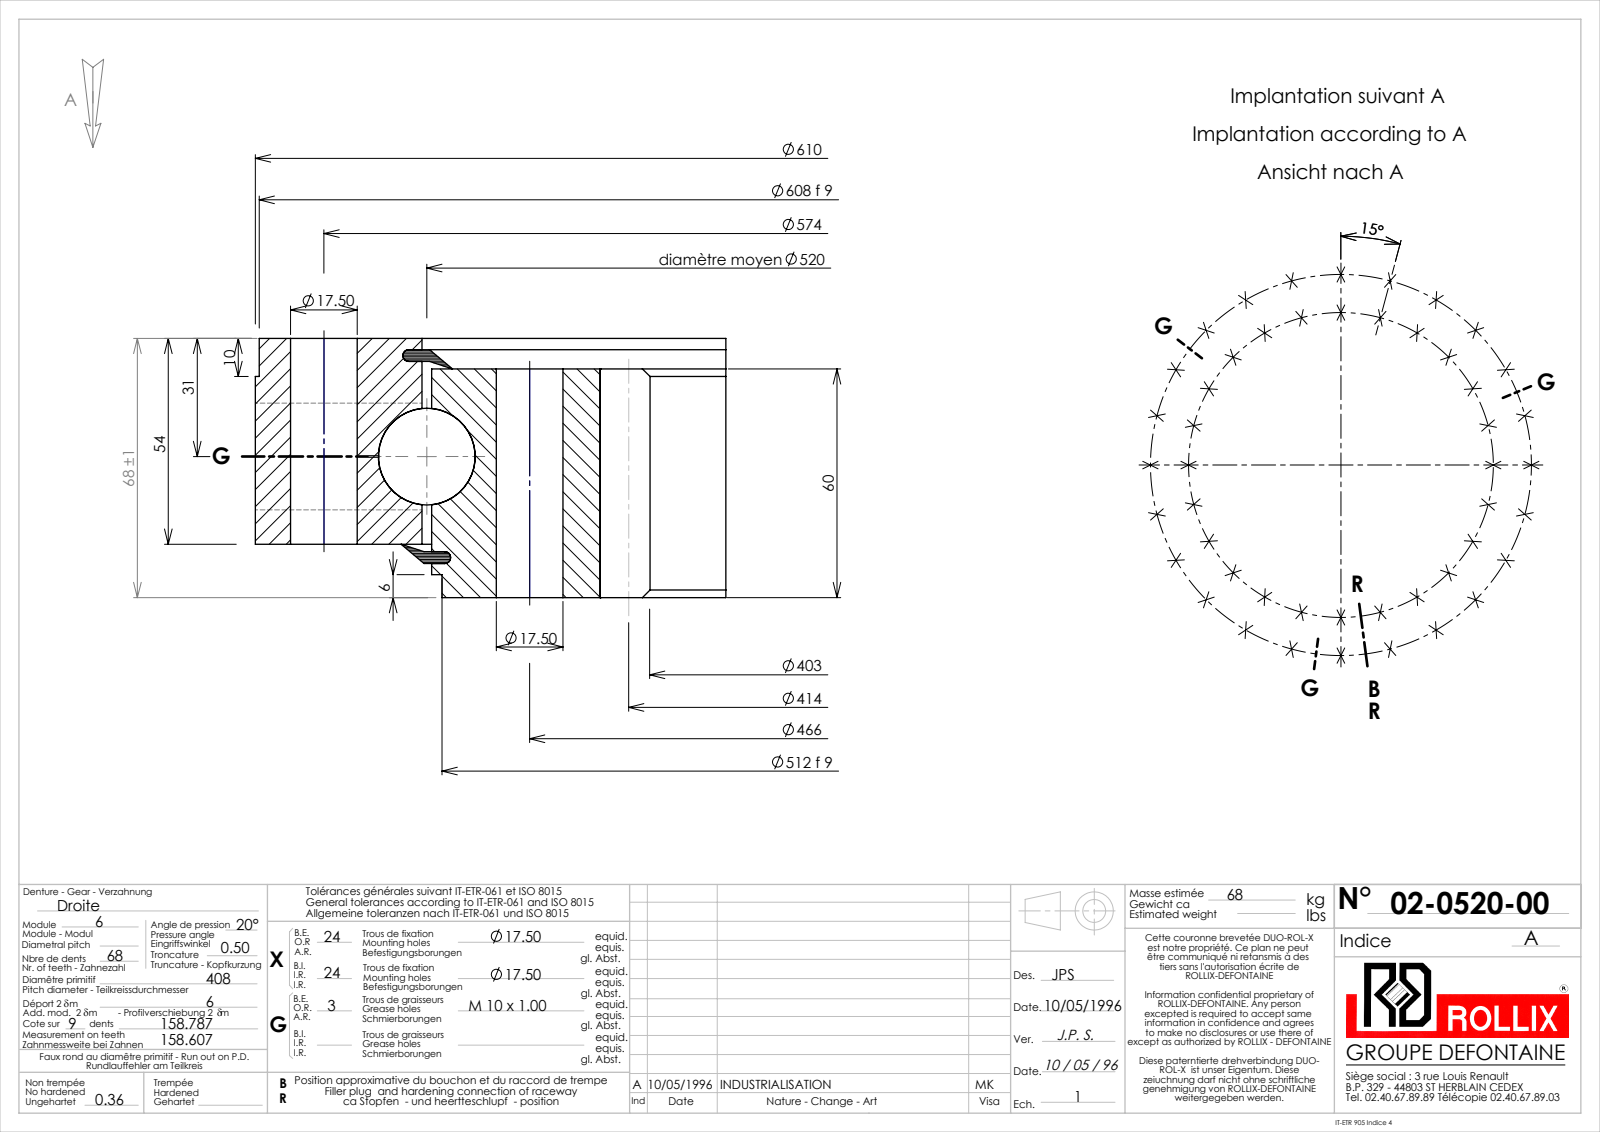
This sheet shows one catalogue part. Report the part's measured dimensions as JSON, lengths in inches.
{"part_name": "02-0520-00", "step_written_by": "SolidWorks 2016 (CONFIG_CONTROL_DESIGN)", "units": "inches", "bodies": {"solids": 5, "faces": 571, "planar": 150, "cylindrical": 257, "other": 164}, "overall_size": [24.016, 24.016, 2.677], "volume_in3": 446.8, "surface_area_in2": 1615, "round_holes": [[0.689, 48], [0.354, 3], [20.572, 1]], "round_bosses_or_shafts": [[24.016, 1], [23.937, 1], [20.372, 1], [20.157, 1]], "partial_cylinders_radius": [[7.933, 1], [8.445, 1]], "face_to_face_distances": [2.126, 0.315, 1.811, 0.551, 2.362, 2.677, 0.077, 1.888, 0.122, 0.199], "hole_center_spacings": [7.021, 14.555, 17.721, 9.173, 12.973, 2.394, 11.169, 15.889]}
